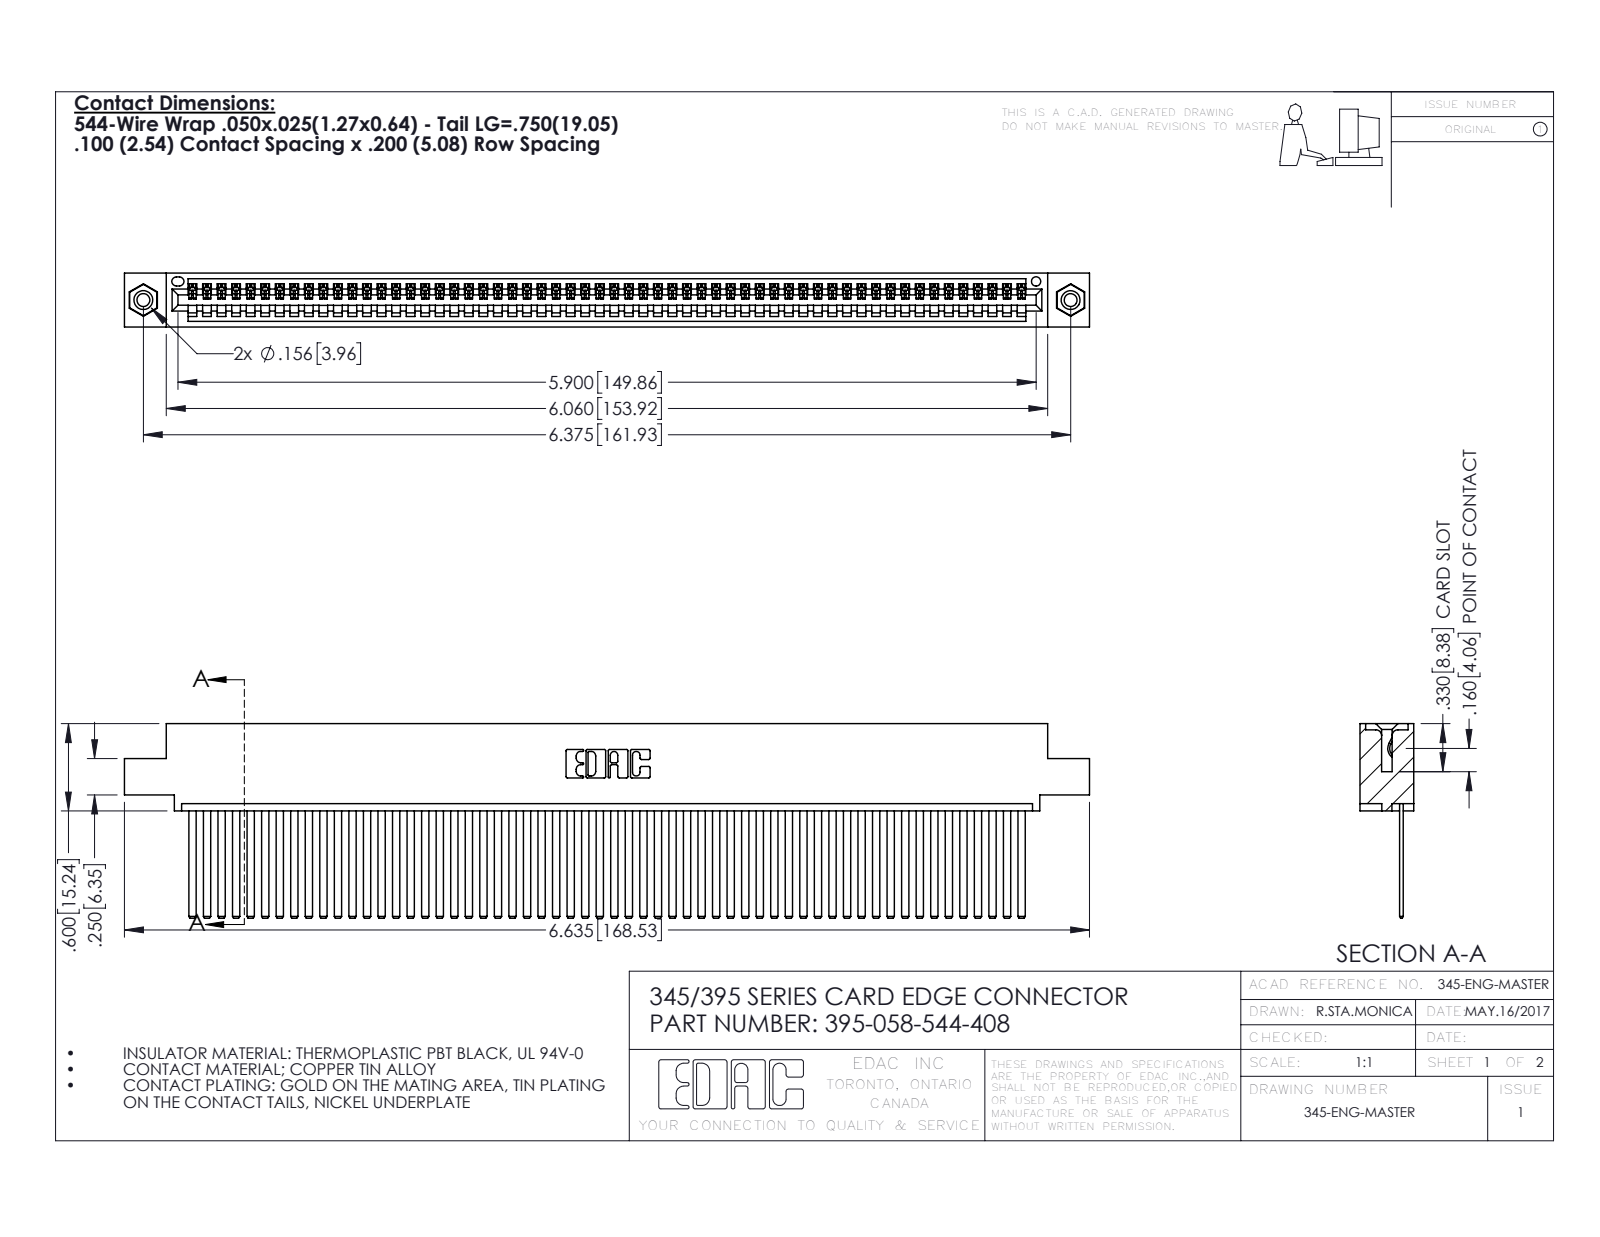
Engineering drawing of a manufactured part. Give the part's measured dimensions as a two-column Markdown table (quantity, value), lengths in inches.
| quantity | value |
| --- | --- |
| part name | 345 Part_0.110 Offset - 0.156 Dia-TI; 395-058-544-408; 345-250-001_345-250-003-102; 345-292-001_345-293-144 |
| STEP written by | SolidWorks 2016 (CONFIG_CONTROL_DESIGN) |
| units | inches |
| bodies | 61 solids, 3206 faces (2204 planar, 986 cylindrical, 16 other) |
| overall size | 6.635 × 1.337 × 0.37 |
| volume | 1.021 in³ |
| surface area | 38.08 in² |
| round holes (diameter × count) | 0.089 × 2, 0.125 × 2, 0.156 × 2, 0.064 × 1 |
| round bosses / shafts (diameter × count) | 0.155 × 2 |
| partial cylindrical surfaces (radius × count) | 0.006 × 116, 0.01 × 22, 0.007 × 6, 0.031 × 6, 0.026 × 3, 0.031 × 2, 0.04 × 2, 0.014 × 1 |
| main face-to-face distances | 0.072, 0.298, 0.025, 0.098, 0.272, 0.37, 0.2, 0.225, 0.149, 0.072 |
| hole center spacings | 0.27, 6.139, 6.375 |
